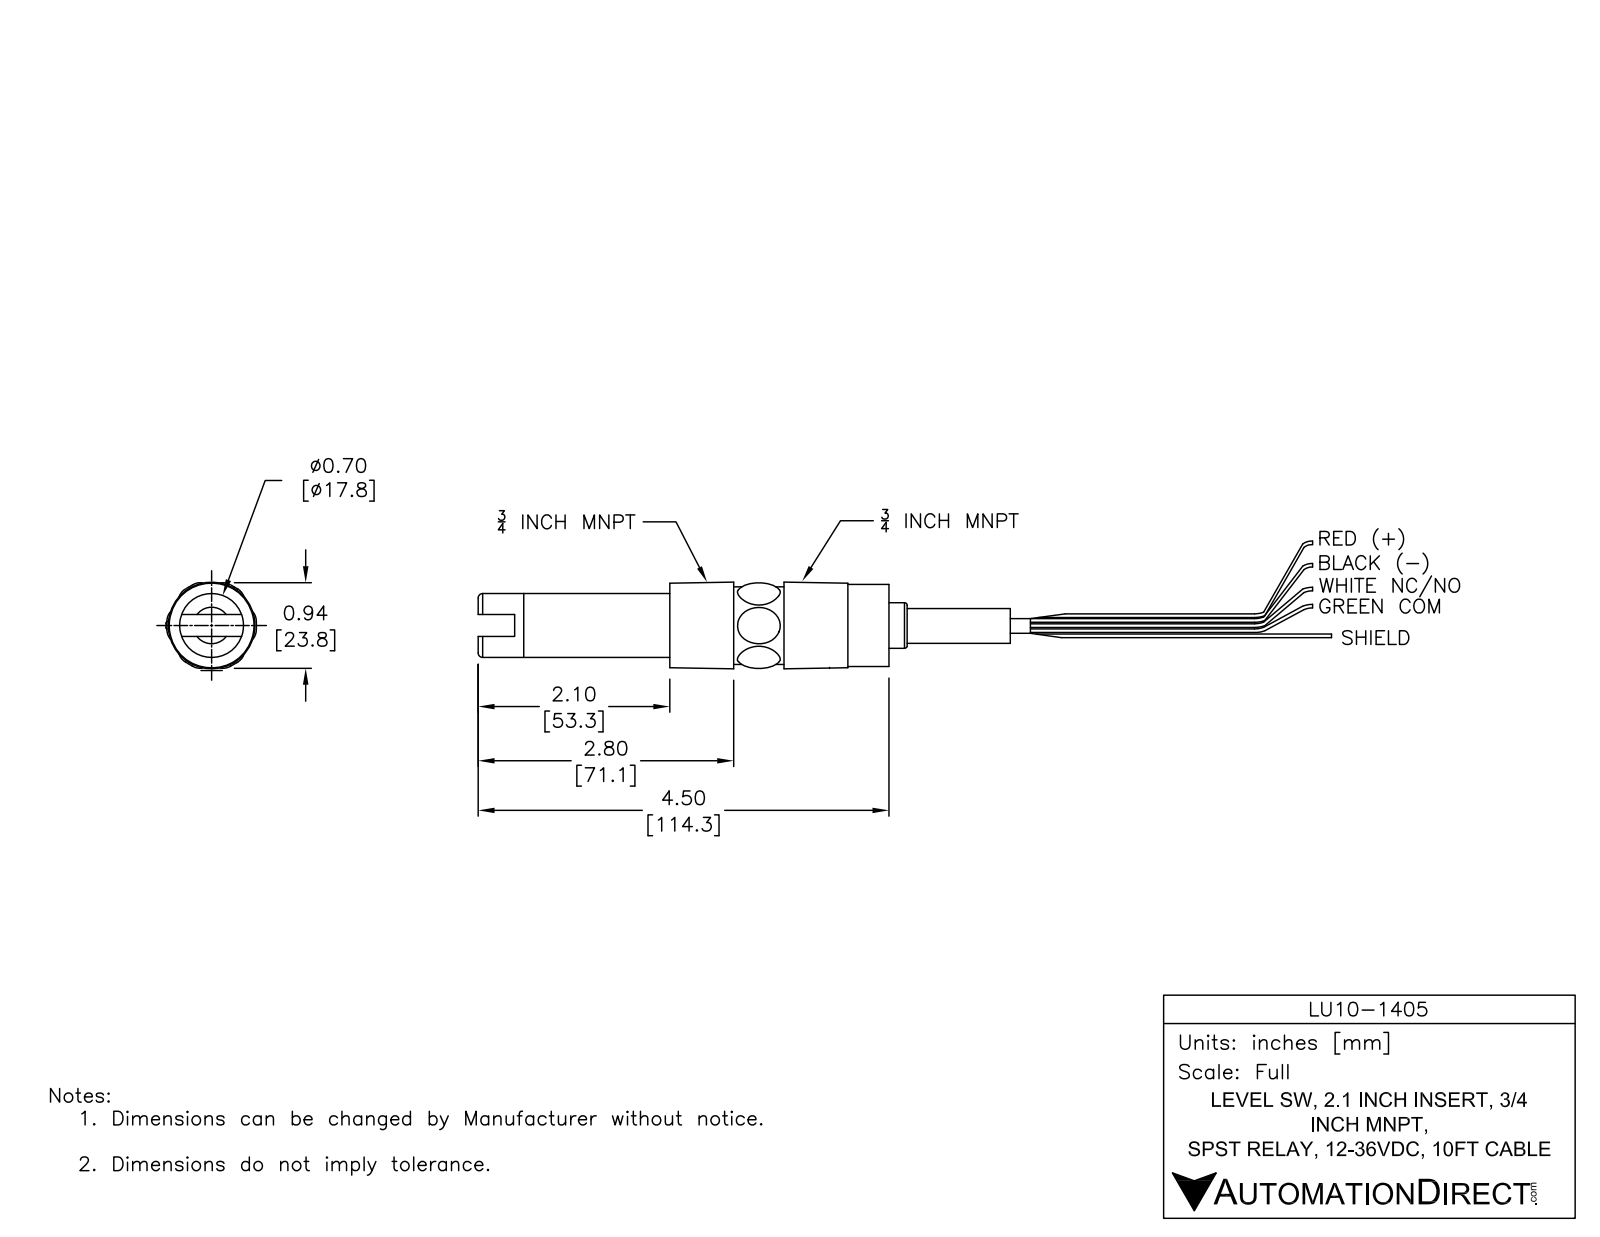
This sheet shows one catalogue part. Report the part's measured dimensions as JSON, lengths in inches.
{"part_name": "LU10-1405", "step_written_by": "SolidWorks 2021 (CONFIG_CONTROL_DESIGN)", "units": "inches", "bodies": {"solids": 2, "faces": 79, "planar": 17, "cylindrical": 6, "other": 56}, "overall_size": [4.981, 1.05, 1.049], "volume_in3": 2.536, "surface_area_in2": 18.62, "round_bosses_or_shafts": [[0.895, 1], [0.722, 1]], "partial_cylinders_radius": [[0.062, 2]], "face_to_face_distances": [0.938, 0.664, 0.25, 0.594, 0.344, 0.344, 0.594, 1.758, 2.422, 0.616]}
